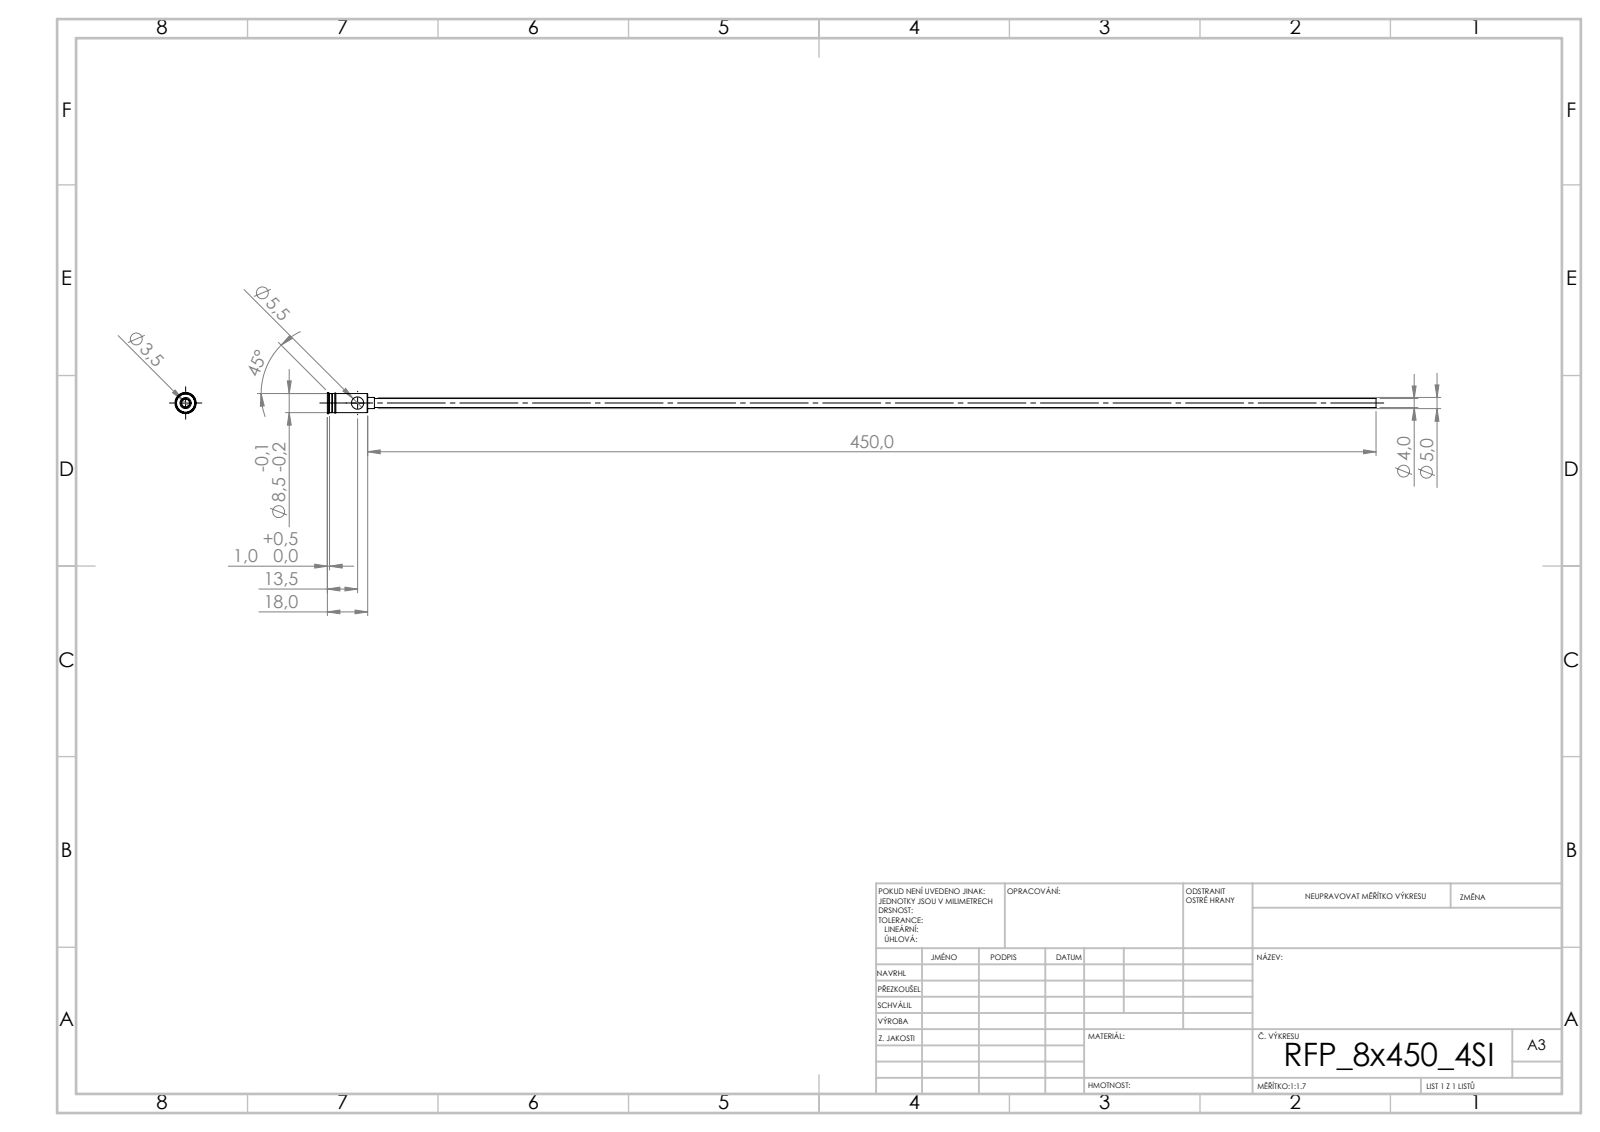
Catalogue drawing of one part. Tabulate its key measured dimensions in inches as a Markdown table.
| quantity | value |
| --- | --- |
| STEP written by | SolidWorks 2019 (CONFIG_CONTROL_DESIGN) |
| units | inches |
| bodies | 1 solid, 44 faces (20 planar, 16 cylindrical, 8 other) |
| overall size | 18.425 × 0.374 × 0.374 |
| volume | 0.131 in³ |
| surface area | 17.6 in² |
| round holes (diameter × count) | 0.138 × 1, 0.217 × 1 |
| round bosses / shafts (diameter × count) | 0.374 × 1, 0.335 × 1, 0.197 × 1, 0.157 × 1 |
| main face-to-face distances | 0.709, 0.63, 0.079, 0.154, 0.618, 0.091, 0.118, 0.736, 0.748, 0.827 |
